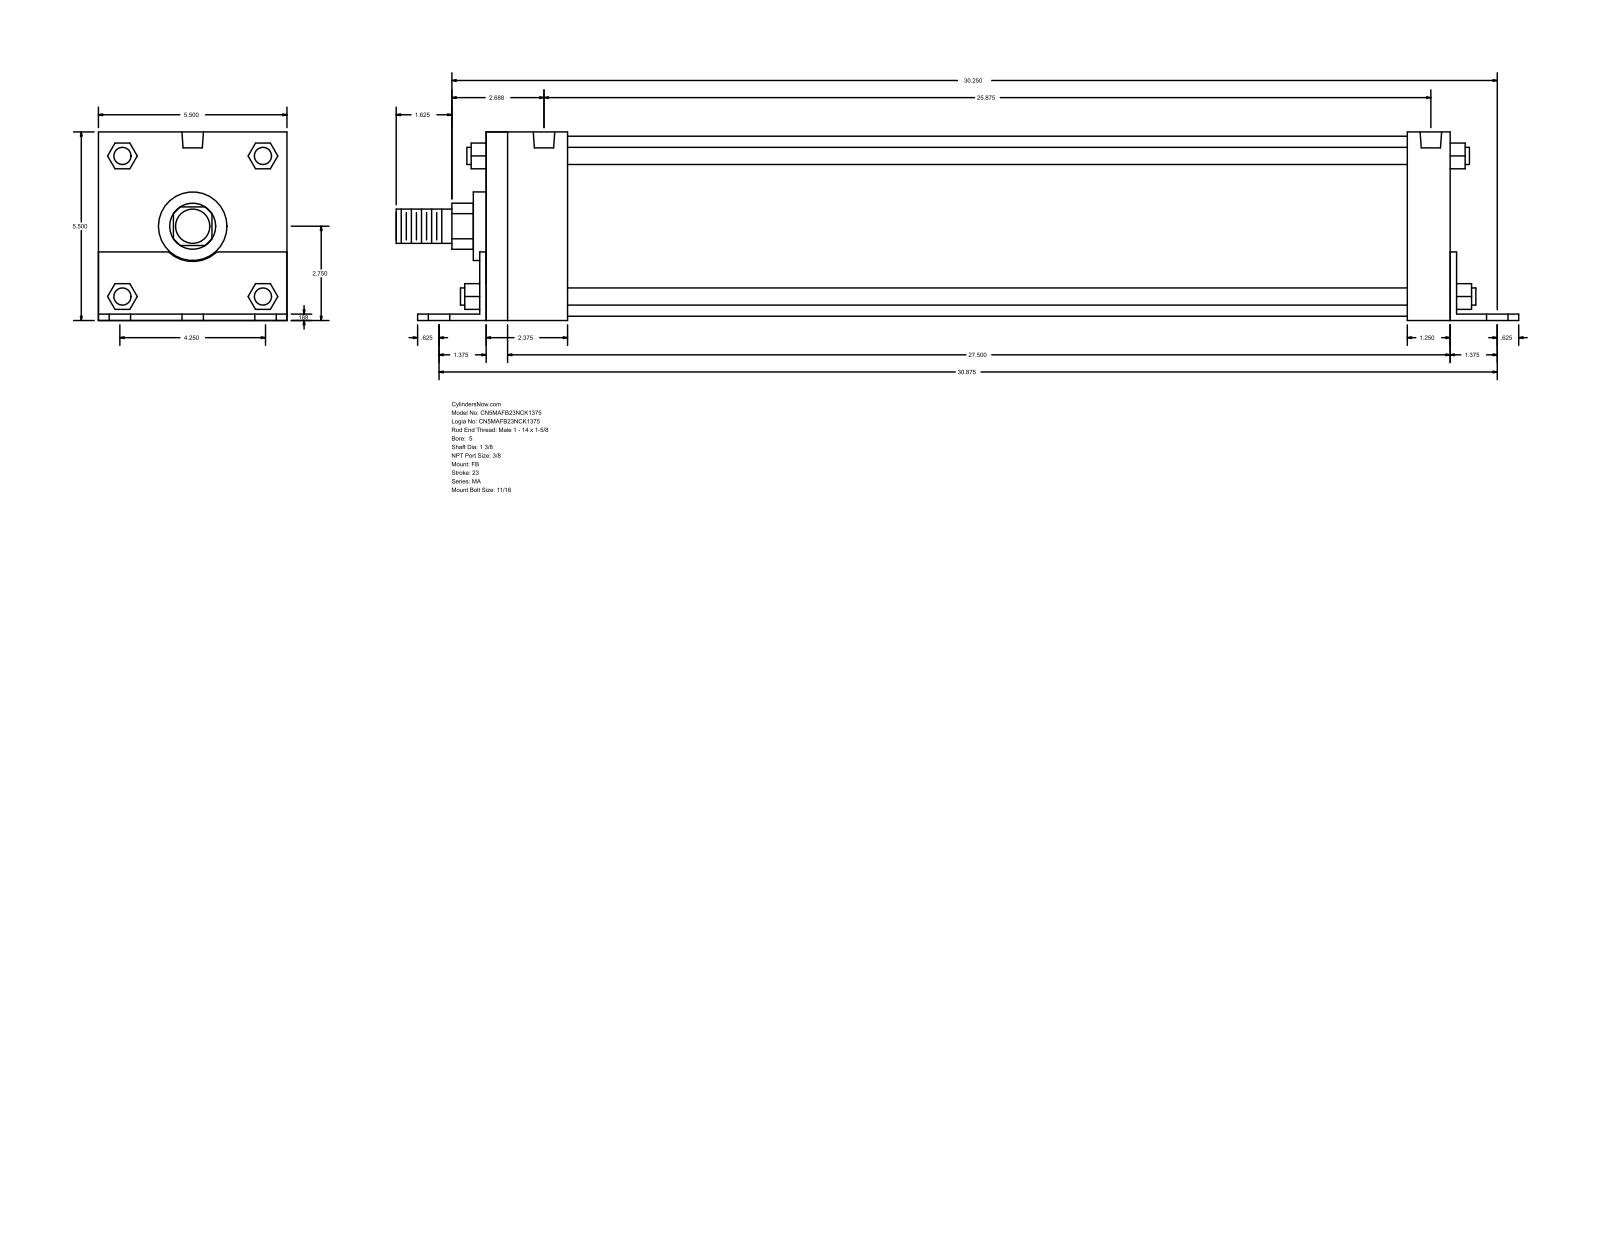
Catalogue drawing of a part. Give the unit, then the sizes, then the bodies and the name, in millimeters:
Units: millimetres
Overall size (bounding box): 831.85 × 139.75 × 139.7
Round holes (diameter × count): ⌀17.46 ×6, ⌀11.11 ×4, ⌀15.93 ×2
Round bosses / shafts (diameter × count): ⌀12.7 ×4, ⌀133.35 ×1, ⌀50.8 ×1, ⌀34.92 ×1, ⌀25.4 ×1
Partial cylindrical surfaces — rounded edges, fillets, slot ends (radius × count): R17.06 ×1, R26.16 ×1
Main face-to-face distances: 139.7, 4.76, 139.75, 4.71, 134.99, 714.37, 4.77, 719.14, 719.13, 723.9
Hole centre spacings: 53.98, 786.09, 784.23, 73.04, 76.33, 94.68, 98.64, 107.96
Bodies: 0 solids, 140 faces (105 planar, 35 cylindrical, 0 other)
Part name (STEP PRODUCT): MA_FB__0500_1.375
STEP written by: GSSL Pune (CONFIG_CONTROL_DESIGN)
